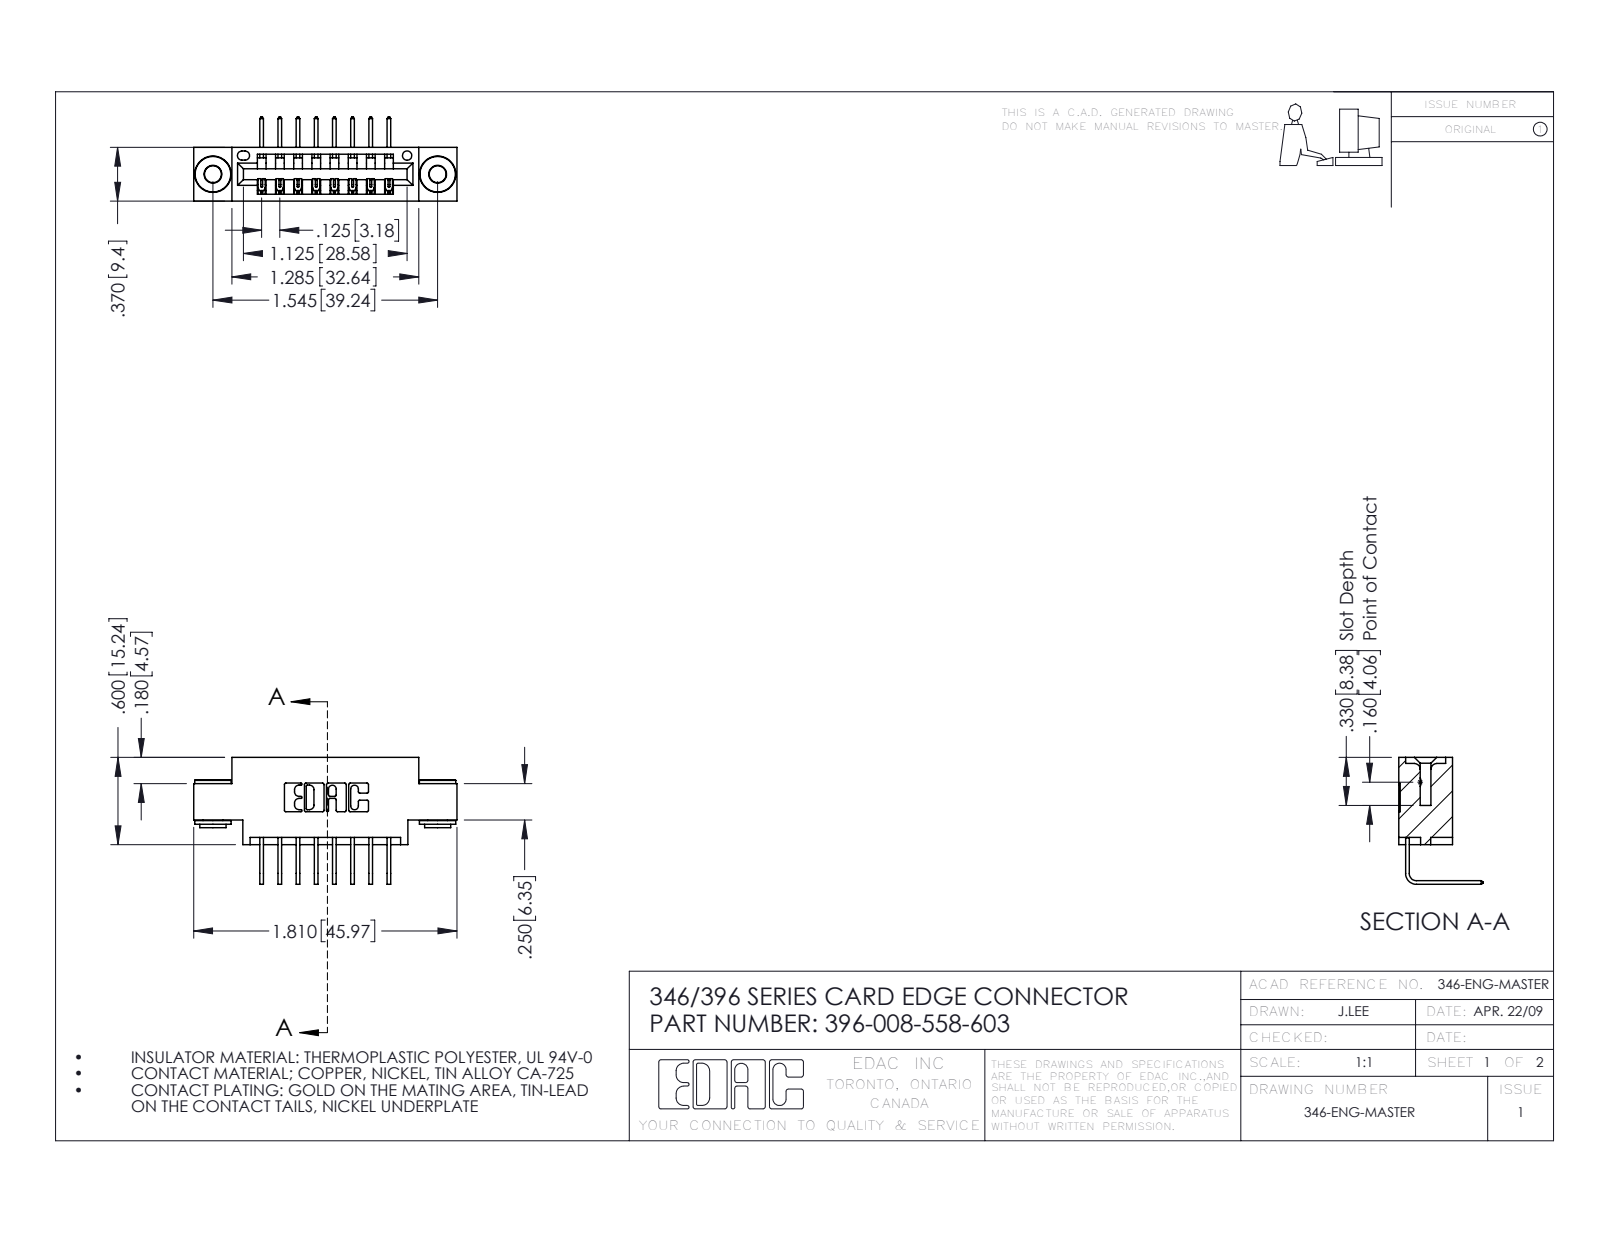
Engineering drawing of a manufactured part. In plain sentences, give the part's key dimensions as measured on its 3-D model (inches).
The part is named "346 Part_0.170 Offset - 0.156 Dia-TH; 345-292-001_558 Tail - 2; 396-008-558-603; 345-250-002_345-250-002-102". Its 3-D file was written by "SolidWorks 2016 (CONFIG_CONTROL_DESIGN)". It is 11 solids with 644 faces: 426 planar, 210 cylindrical and 8 other. Overall it measures 1.81 by 0.873 by 0.58 inches. Its volume is 0.248 cubic inches and its surface area 8.127 square inches. Round holes: 2 of diameter 0.116, 2 of diameter 0.156, 1 of diameter 0.064. Round bosses or shafts: 2 of diameter 0.25, 2 of diameter 0.18, 2 of diameter 0.136. Partial cylindrical surfaces (rounded edges, fillets, slot ends): 22 of radius 0.01, 16 of radius 0.006, 6 of radius 0.007, 6 of radius 0.031, 3 of radius 0.026, 2 of radius 0.031, 2 of radius 0.04, 1 of radius 0.014. The main face-to-face distances are 0.25, 0.37, 0.322, 0.048, 0.025, 0.298, 0.148, 0.222, 0.1, 0.174. The hole center spacings are 0.246, 1.341, 1.545.
